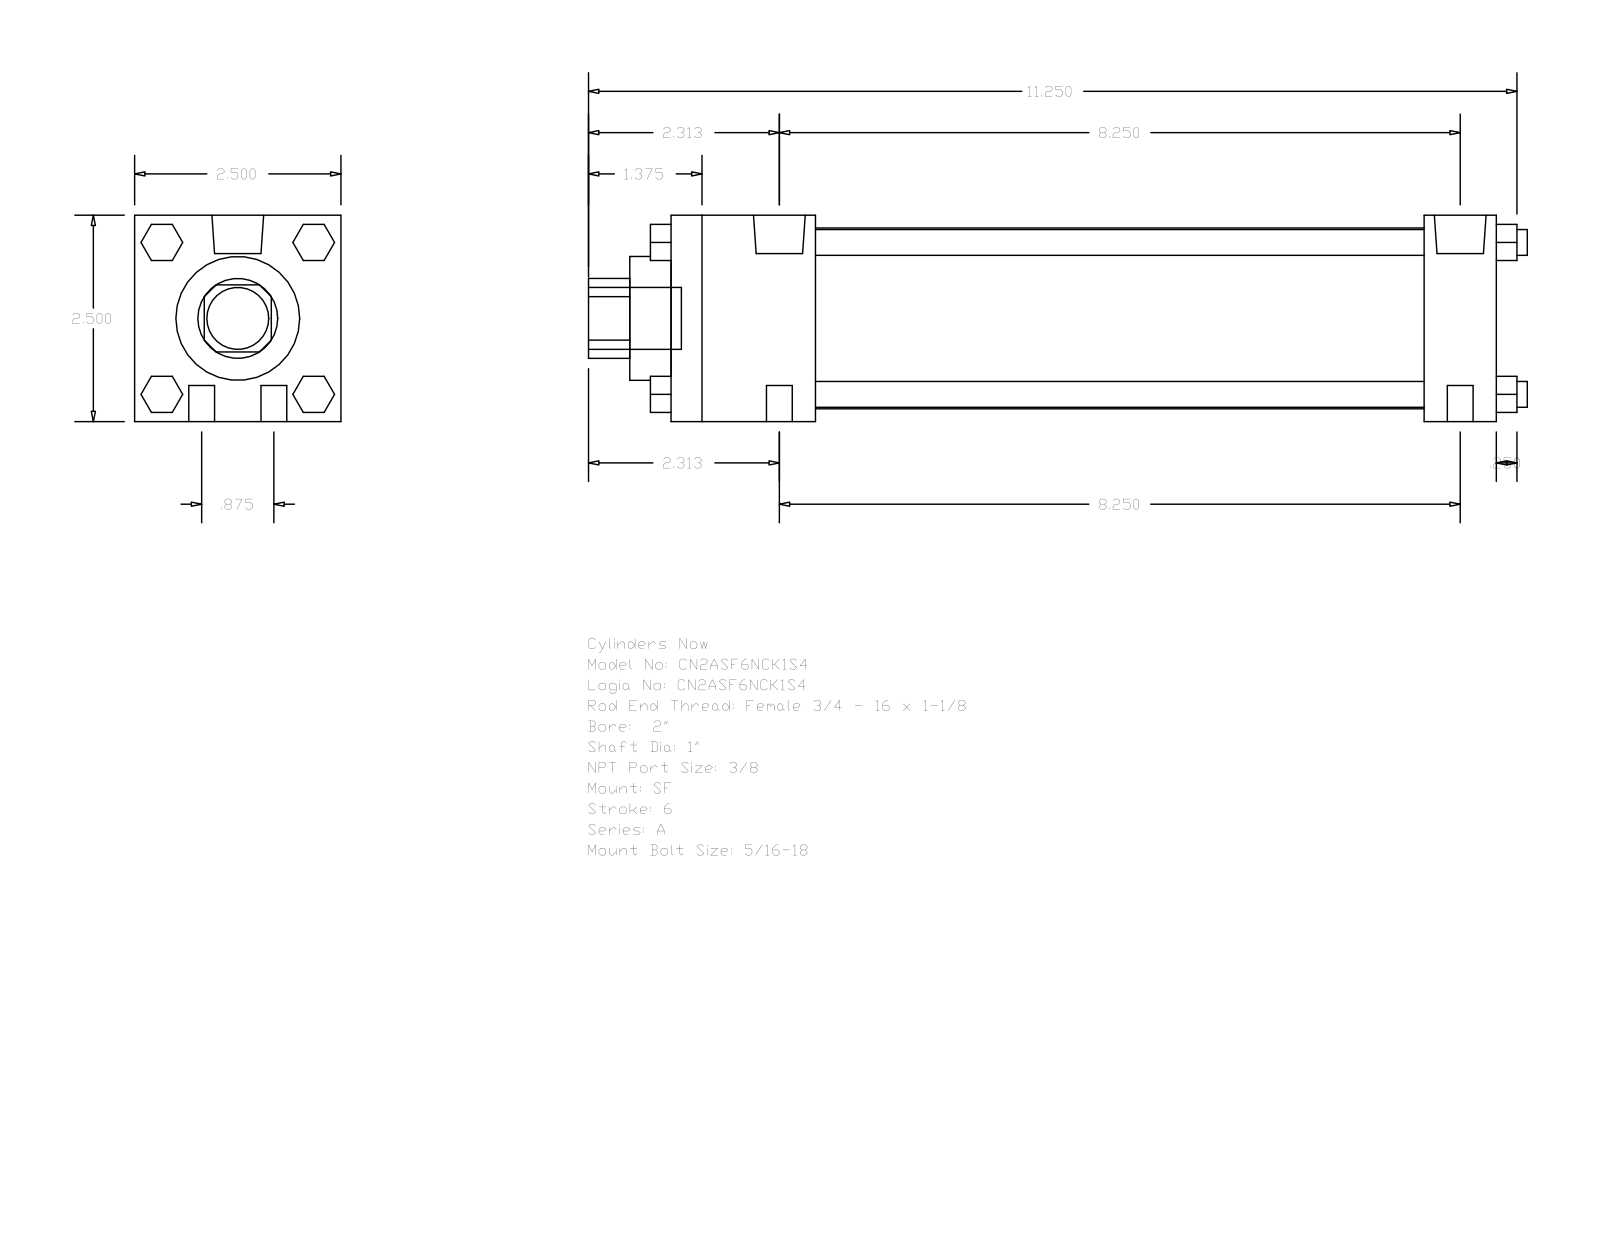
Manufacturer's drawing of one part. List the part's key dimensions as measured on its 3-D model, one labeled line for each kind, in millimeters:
Part name (STEP PRODUCT): A_SF__0200_1
STEP written by: GSSL Pune (CONFIG_CONTROL_DESIGN)
Units: millimetres
Bodies: 0 solids, 124 faces (94 planar, 30 cylindrical, 0 other)
Overall size (bounding box): 288.93 × 63.5 × 63.5
Round holes (diameter × count): ⌀25.4 ×1, ⌀38.1 ×1, ⌀55.63 ×1
Round bosses / shafts (diameter × count): ⌀7.94 ×8, ⌀15.93 ×2, ⌀5.56 ×2, ⌀19.05 ×1
Partial cylindrical surfaces — rounded edges, fillets, slot ends (radius × count): R12.29 ×1
Main face-to-face distances: 63.5, 254, 231.78, 22.22, 44.45, 187.33, 209.55, 12.7, 266.7, 6.35
